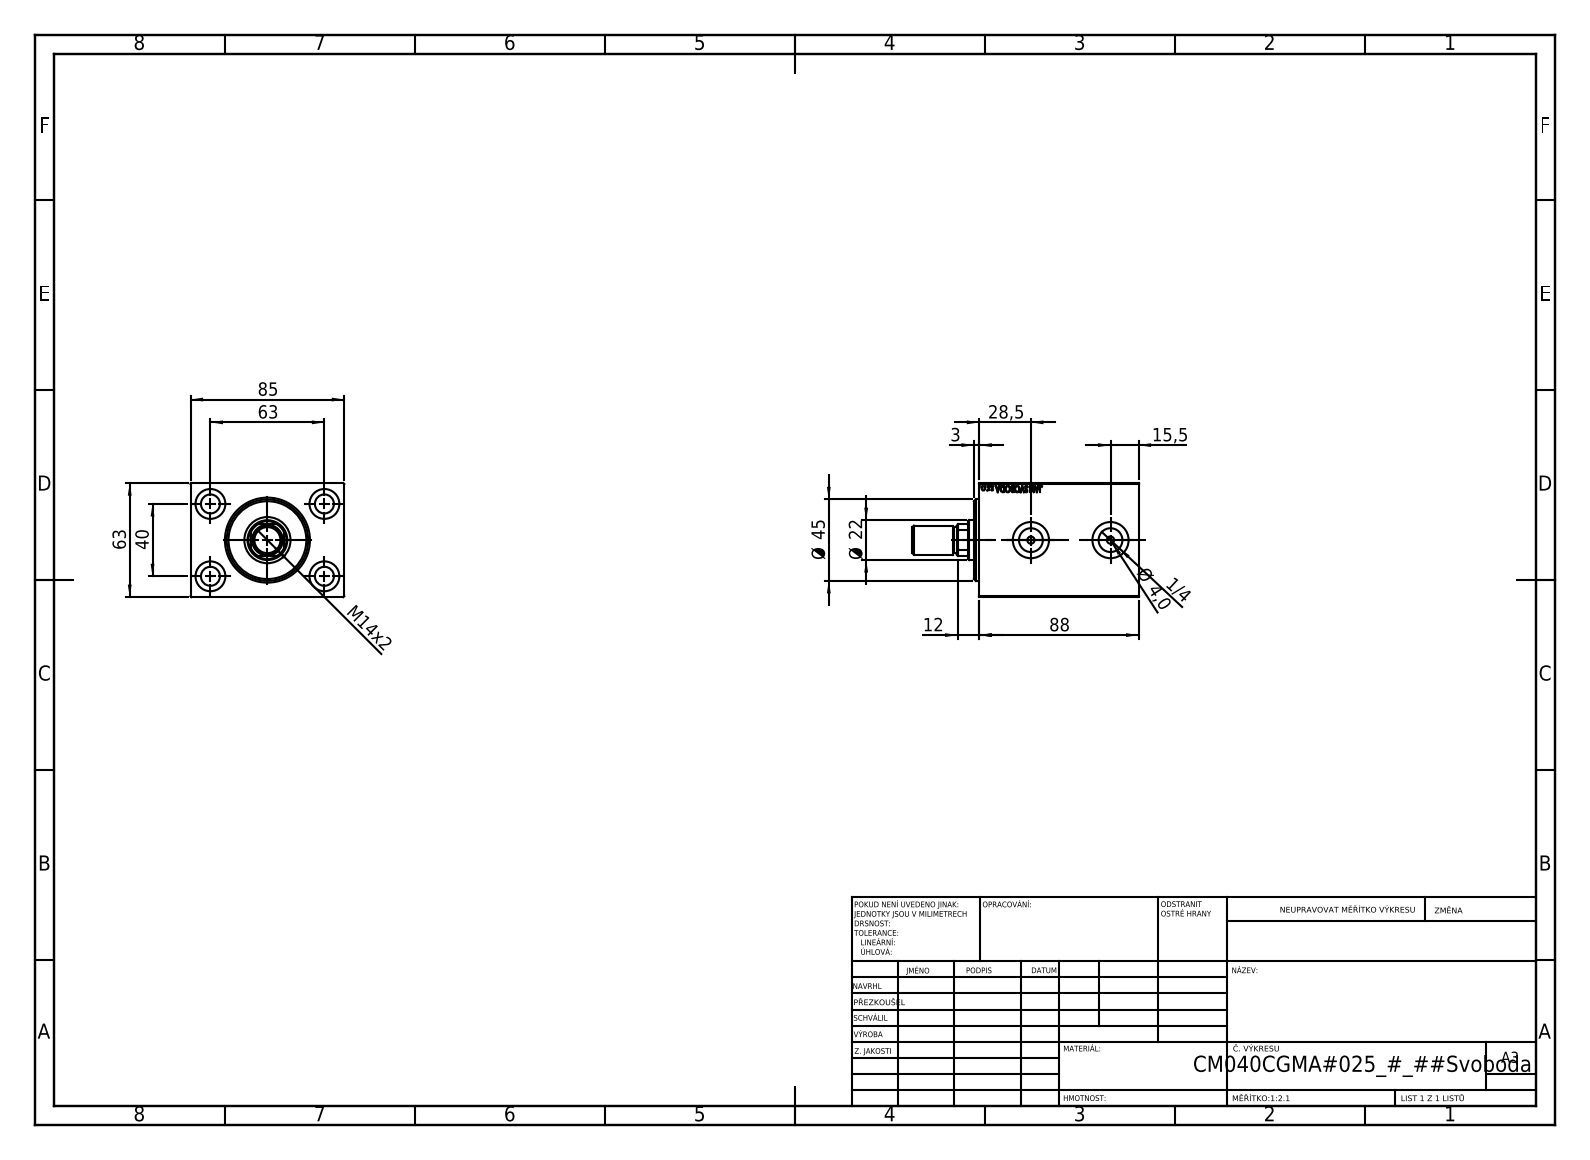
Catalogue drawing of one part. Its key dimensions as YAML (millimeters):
part_name: "V450CM_MALE_METRIC; V450CM_VC_B; V450CM_C_Body; V450CM_C_VCP"
step_written_by: "SolidWorks 2019 (CONFIG_CONTROL_DESIGN)"
units: millimeters
bodies: {solids: 4, faces: 876, planar: 412, cylindrical: 64, other: 400}
overall_size: [125, 85, 63]
volume: 413527
surface_area: 78950
round_holes:
  - {diameter: 10.5, count: 4}
  - {diameter: 16.5, count: 4}
  - {diameter: 4, count: 2}
  - {diameter: 13.16, count: 2}
  - {diameter: 20, count: 2}
  - {diameter: 12.5, count: 1}
  - {diameter: 22, count: 1}
  - {diameter: 25.5, count: 1}
  - {diameter: 40, count: 1}
  - {diameter: 42, count: 1}
  - {diameter: 45, count: 1}
round_bosses_or_shafts:
  - {diameter: 16, count: 1}
  - {diameter: 14, count: 1}
partial_cylinders:
  - {radius: 10.5, count: 1}
face_to_face_distances: [63, 85, 12, 76, 88, 40, 64, 11, 37, 25]
hole_center_spacings: [37.31, 40, 63, 74.63, 44]
